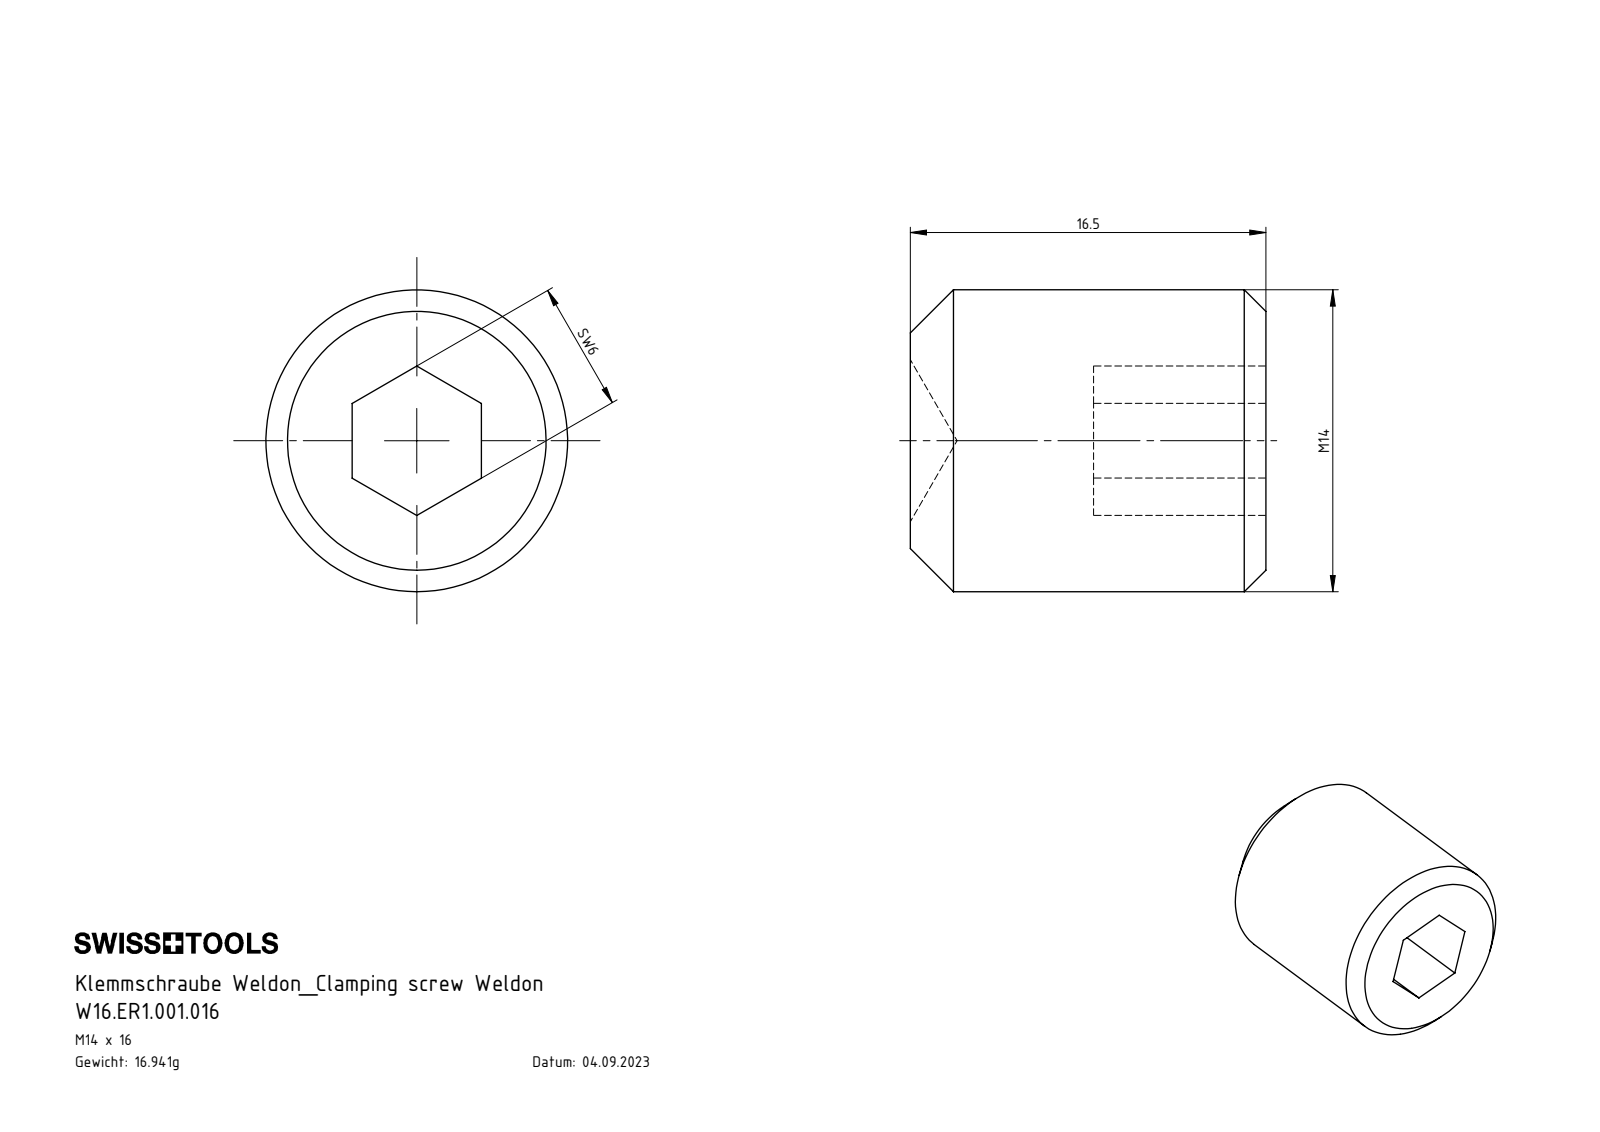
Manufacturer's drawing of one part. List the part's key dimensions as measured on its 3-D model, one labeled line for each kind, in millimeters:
Part name (STEP PRODUCT): W16.ER1.001.016
STEP written by: SolidWorks 2017 (AUTOMOTIVE_DESIGN)
Units: millimetres
Bodies: 1 solid, 17 faces (9 planar, 2 cylindrical, 6 other)
Overall size (bounding box): 16.5 × 14 × 14
Volume: 2 158 mm³ · Surface area: 1 123 mm²
Round bosses / shafts (diameter × count): ⌀14 ×1
Main face-to-face distances: 6, 16.5, 8, 8.5
